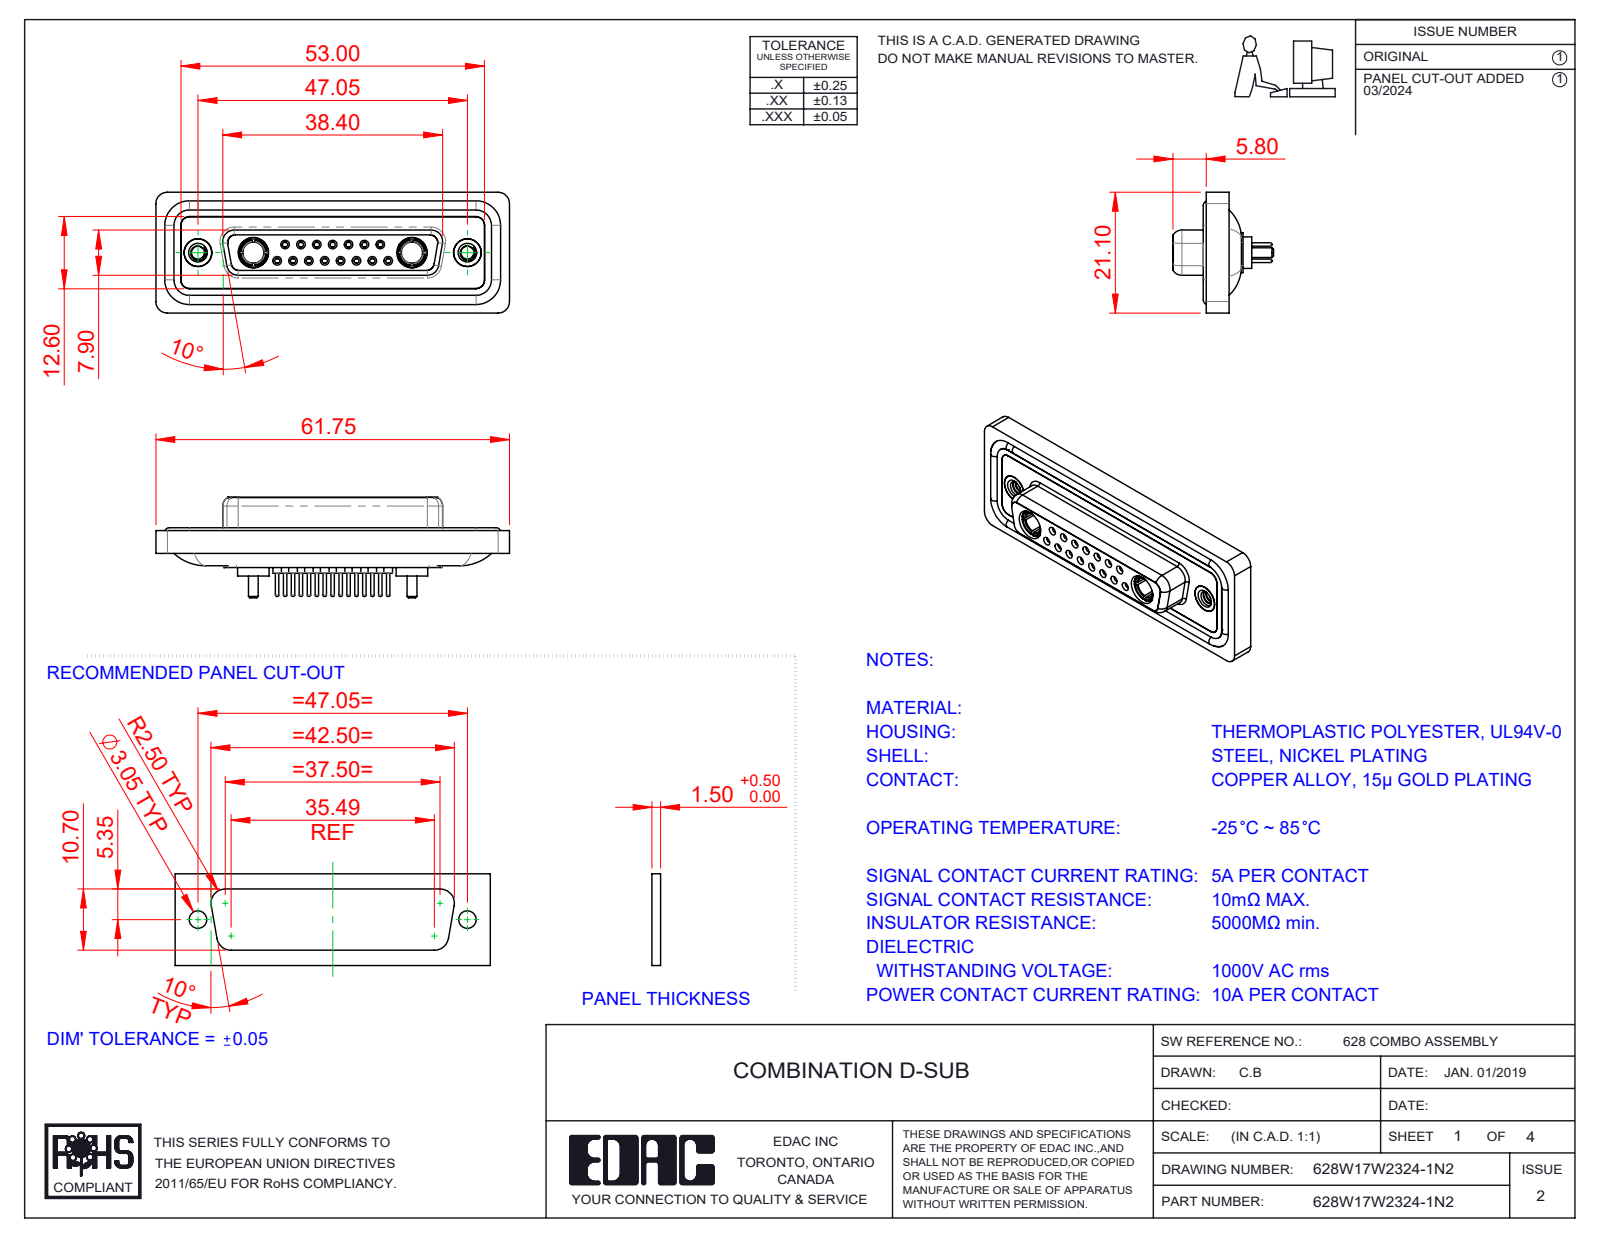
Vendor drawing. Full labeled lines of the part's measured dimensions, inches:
Part name (STEP PRODUCT): 628Combo Shell Rear_25 Contacts; 628Combo Shell Front_25 Contacts; 628Combo Contact Row 1_24; 628Combo Contact Row 2_24 (+5 more)
STEP written by: SolidWorks 2023 (CONFIG_CONTROL_DESIGN)
Units: inches
Bodies: 26 solids, 1359 faces (388 planar, 519 cylindrical, 452 other)
Overall size (bounding box): 2.431 × 0.831 × 0.691
Volume: 0.506 in³ · Surface area: 21.44 in²
Round holes (diameter × count): ⌀0.035 ×15, ⌀0.043 ×15, ⌀0.059 ×15, ⌀0.079 ×15, ⌀0.063 ×8, ⌀0.067 ×7, ⌀0.191 ×4, ⌀0.089 ×2, ⌀0.146 ×2, ⌀0.157 ×2, ⌀0.159 ×2, ⌀0.197 ×2
Round bosses / shafts (diameter × count): ⌀0.087 ×15, ⌀0.024 ×15, ⌀0.063 ×11, ⌀0.217 ×2, ⌀0.205 ×2, ⌀0.195 ×2, ⌀0.195 ×2, ⌀0.189 ×2
Partial cylindrical surfaces — rounded edges, fillets, slot ends (radius × count): R0.059 ×22, R0.079 ×18, R0.053 ×8, R0.063 ×8, R0.01 ×4, R0.02 ×4, R0.024 ×4, R0.026 ×4
Main face-to-face distances: 0.016, 0.071, 0.293, 0.222, 0.26, 0.02, 0.278, 0.063, 0.114, 0.043
Hole centre spacings: 0.124, 0.109, 0.327, 0.218, 0.198, 0.198, 0.295, 0.436
